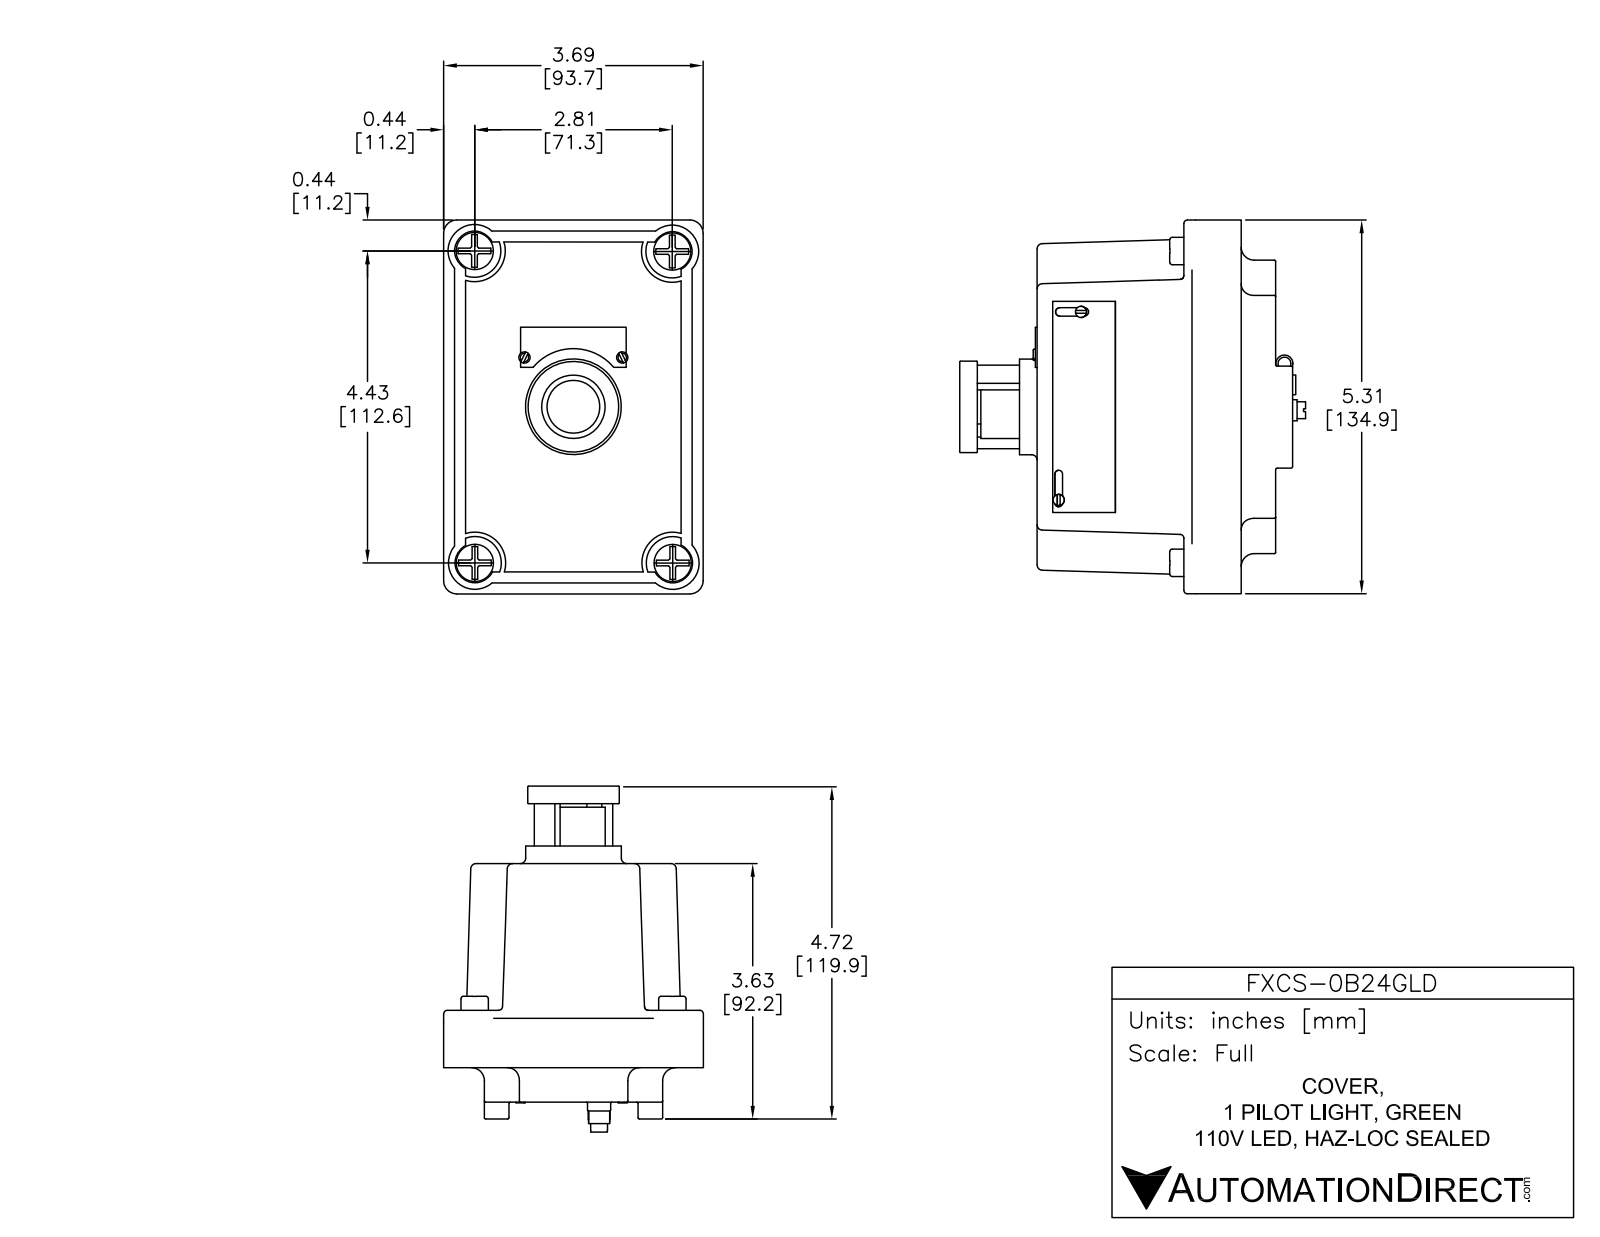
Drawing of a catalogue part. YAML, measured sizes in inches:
part_name: "FXCS-0B24GLD"
step_written_by: "SolidWorks 2015 (AUTOMOTIVE_DESIGN)"
units: inches
bodies: {solids: 1, faces: 696, planar: 288, cylindrical: 147, other: 261}
overall_size: [5.31, 4.989, 3.69]
volume: 48.88
surface_area: 99.55
round_holes:
  - {diameter: 0.16, count: 8}
  - {diameter: 0.198, count: 1}
  - {diameter: 0.94, count: 1}
round_bosses_or_shafts:
  - {diameter: 0.16, count: 6}
  - {diameter: 0.39, count: 4}
  - {diameter: 1.36, count: 1}
  - {diameter: 1.3, count: 1}
  - {diameter: 0.9, count: 1}
  - {diameter: 0.33, count: 1}
  - {diameter: 0.3, count: 1}
  - {diameter: 0.24, count: 1}
partial_cylinders:
  - {radius: 0.02, count: 22}
  - {radius: 0.05, count: 12}
  - {radius: 0.055, count: 4}
  - {radius: 0.06, count: 4}
  - {radius: 0.075, count: 4}
  - {radius: 0.185, count: 4}
  - {radius: 0.42, count: 4}
  - {radius: 0.653, count: 3}
face_to_face_distances: [3.39, 0.49, 2.9, 0.02, 3.69, 0.578, 3.111, 1.19, 0.7, 2.2]
hole_center_spacings: [0.25, 2.197, 0.5, 2.183, 2.239, 0.75, 1.092, 1.115]
